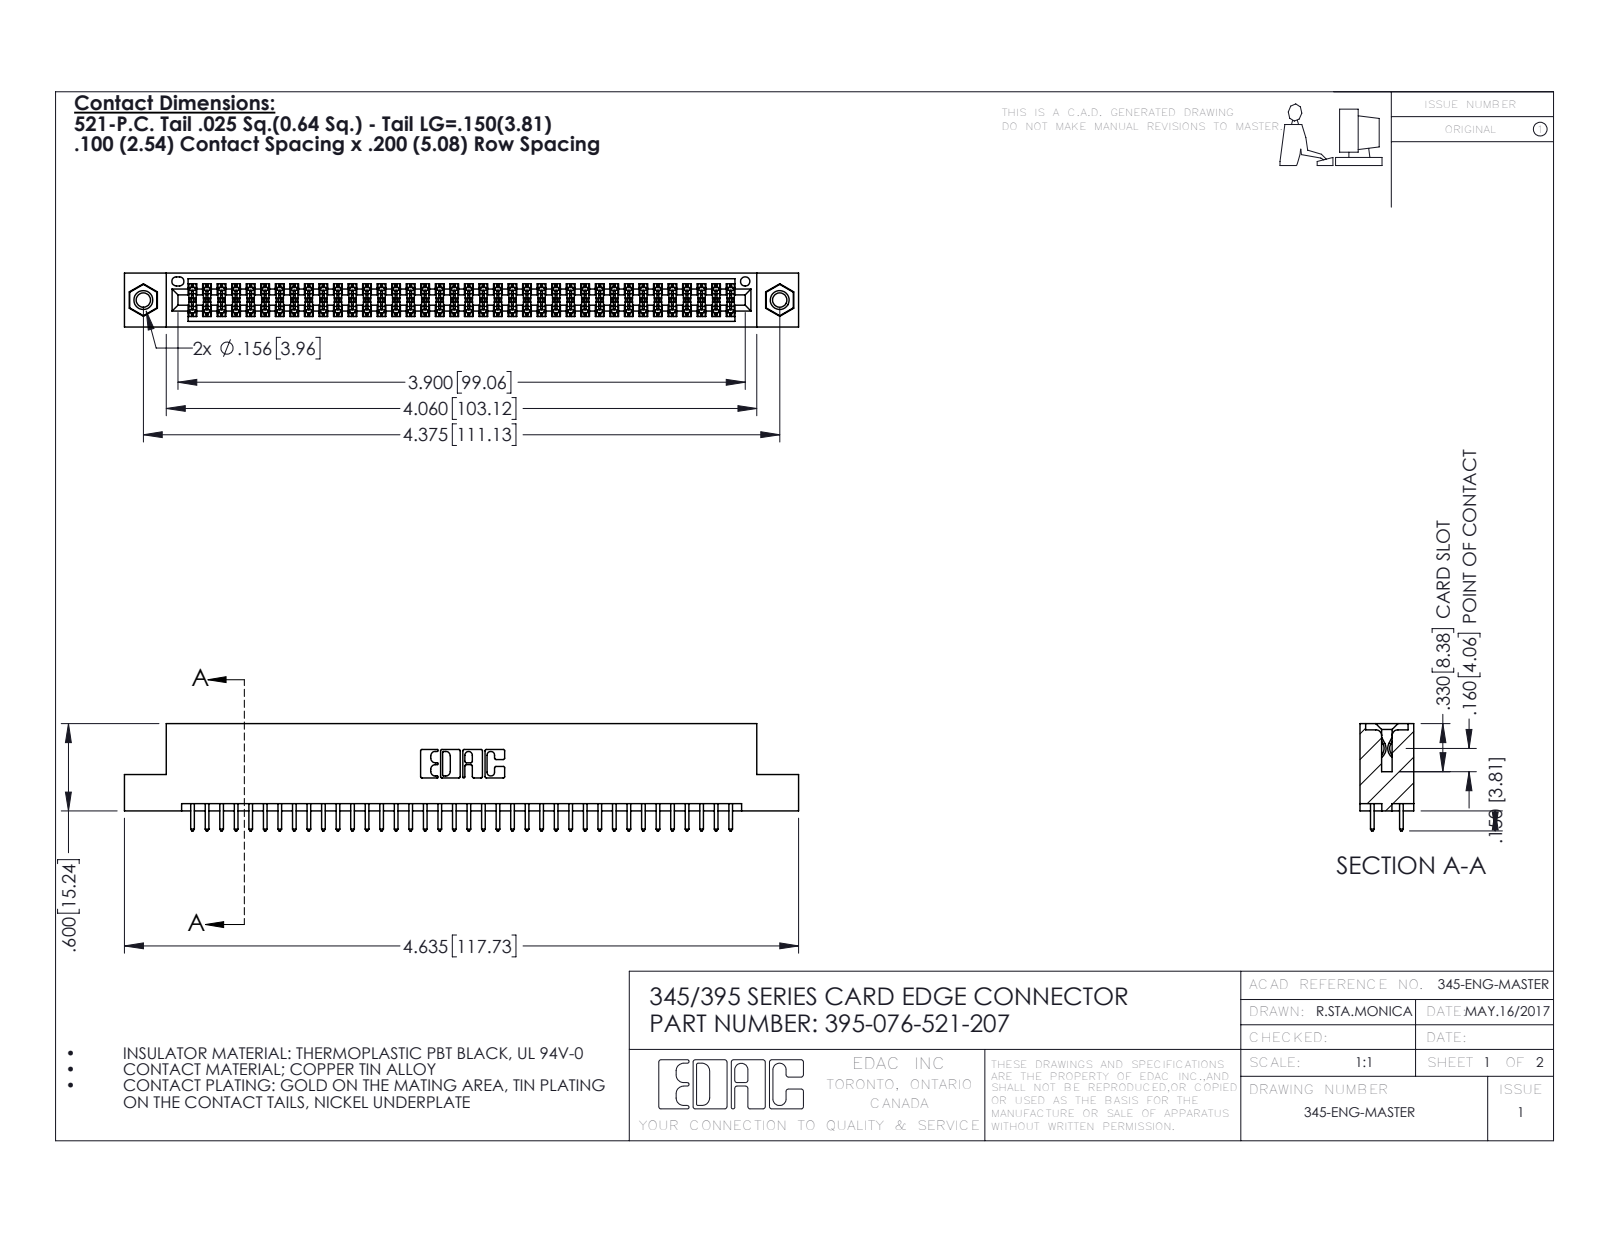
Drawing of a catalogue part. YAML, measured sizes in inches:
part_name: "345 Part_Flush Mounting Lugs - 0.156 Dia-TI; 345-250-001_345-250-005-103; 345-292-001_345-293-121; 395-076-521-207"
step_written_by: "SolidWorks 2016 (CONFIG_CONTROL_DESIGN)"
units: inches
bodies: {solids: 79, faces: 3986, planar: 2620, cylindrical: 1350, other: 16}
overall_size: [4.635, 0.737, 0.37]
volume: 0.693
surface_area: 25.63
round_holes:
  - {diameter: 0.098, count: 2}
  - {diameter: 0.125, count: 2}
  - {diameter: 0.156, count: 2}
  - {diameter: 0.064, count: 1}
round_bosses_or_shafts:
  - {diameter: 0.155, count: 2}
partial_cylinders:
  - {radius: 0.006, count: 114}
  - {radius: 0.01, count: 76}
  - {radius: 0.01, count: 22}
  - {radius: 0.007, count: 6}
  - {radius: 0.031, count: 6}
  - {radius: 0.026, count: 3}
  - {radius: 0.014, count: 2}
  - {radius: 0.019, count: 2}
face_to_face_distances: [0.072, 0.298, 0.2, 0.37, 0.098, 0.272, 0.025, 0.225, 0.175, 0.149]
hole_center_spacings: [0.27, 4.139, 4.375]
